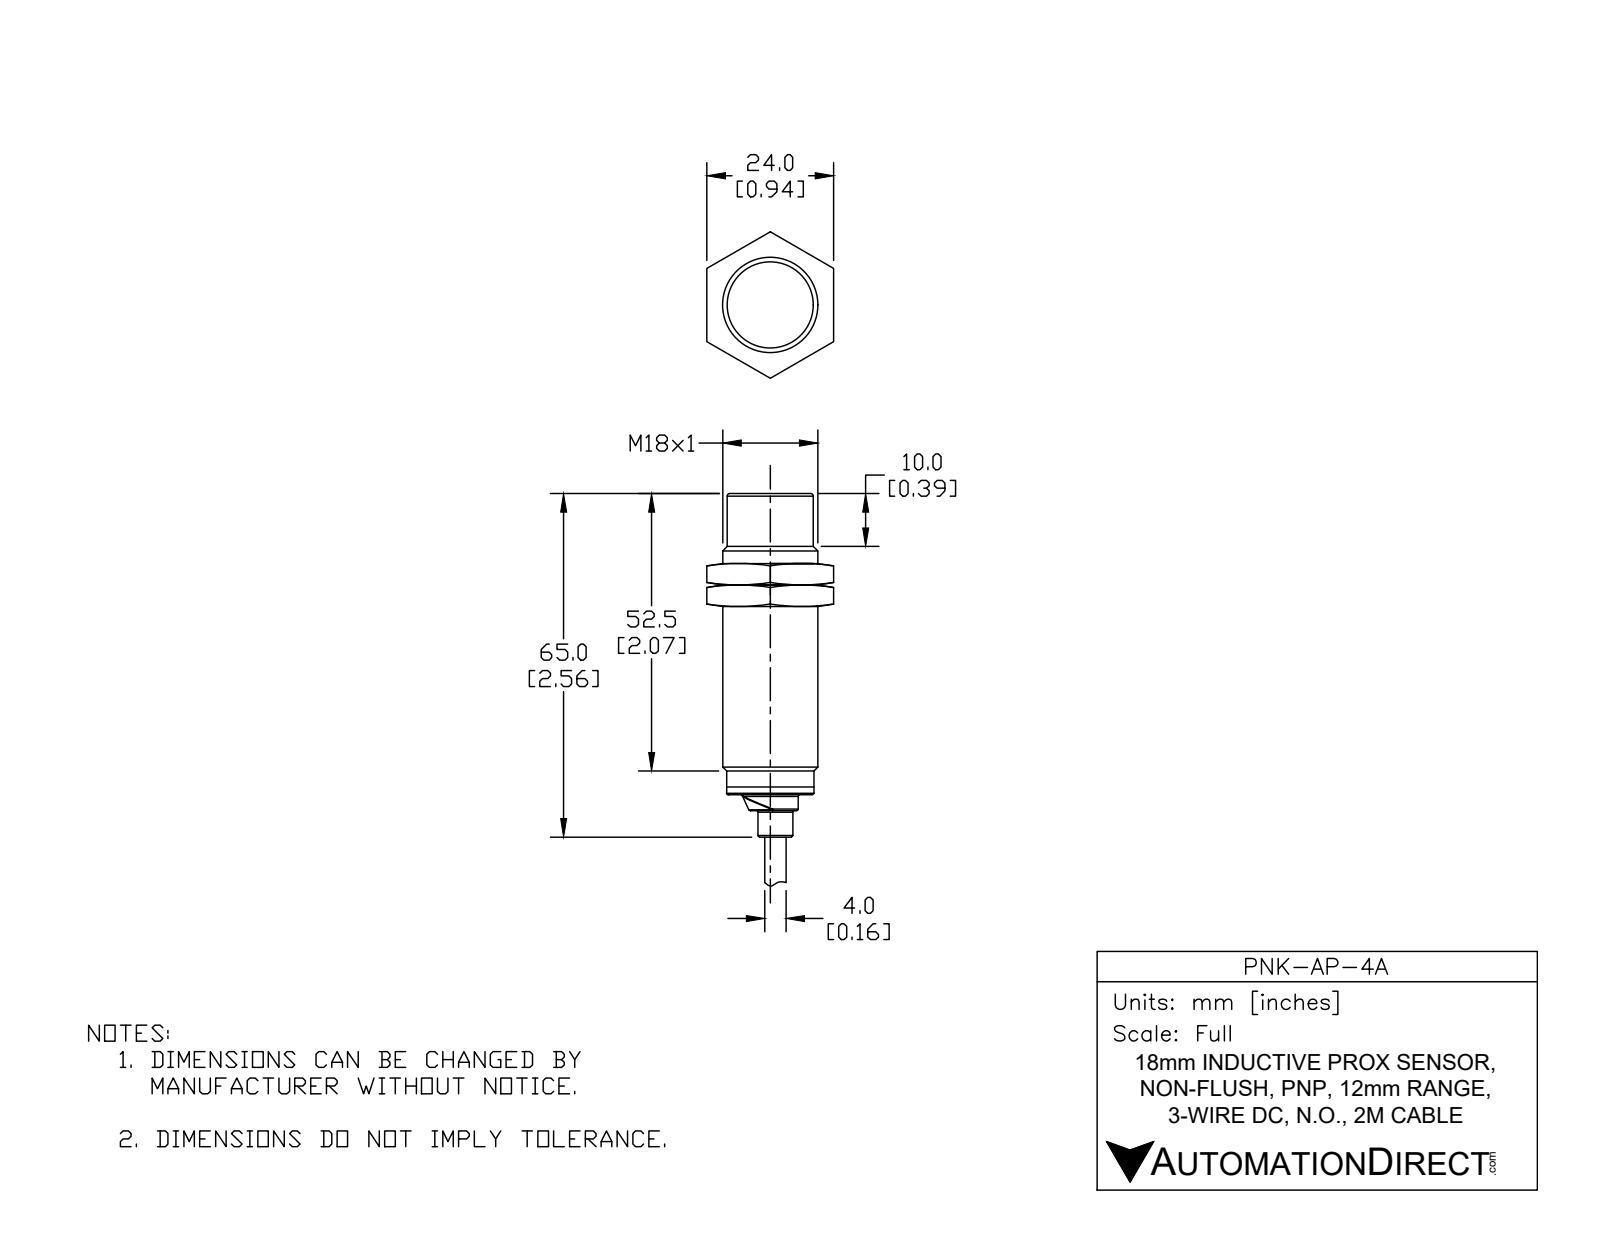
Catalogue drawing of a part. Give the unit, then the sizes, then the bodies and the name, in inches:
Units: inches
Overall size (bounding box): 4.559 × 0.709 × 0.709
Round holes (diameter × count): ⌀0.634 ×1
Round bosses / shafts (diameter × count): ⌀0.709 ×1, ⌀0.65 ×1, ⌀0.65 ×1, ⌀0.633 ×1, ⌀0.417 ×1, ⌀0.26 ×1, ⌀0.157 ×1
Partial cylindrical surfaces — rounded edges, fillets, slot ends (radius × count): R0.079 ×1, R0.081 ×1, R0.091 ×1
Main face-to-face distances: 2.244, 2.362, 0.118, 2.559, 0.315, 0.197, 4.559, 2.315, 2.197, 2
Volume: 0.936 in³ · Surface area: 7.094 in²
Bodies: 1 solid, 76 faces (18 planar, 20 cylindrical, 38 other)
Part name (STEP PRODUCT): PNK-AP-4A
STEP written by: SolidWorks 2017 (AUTOMOTIVE_DESIGN)
